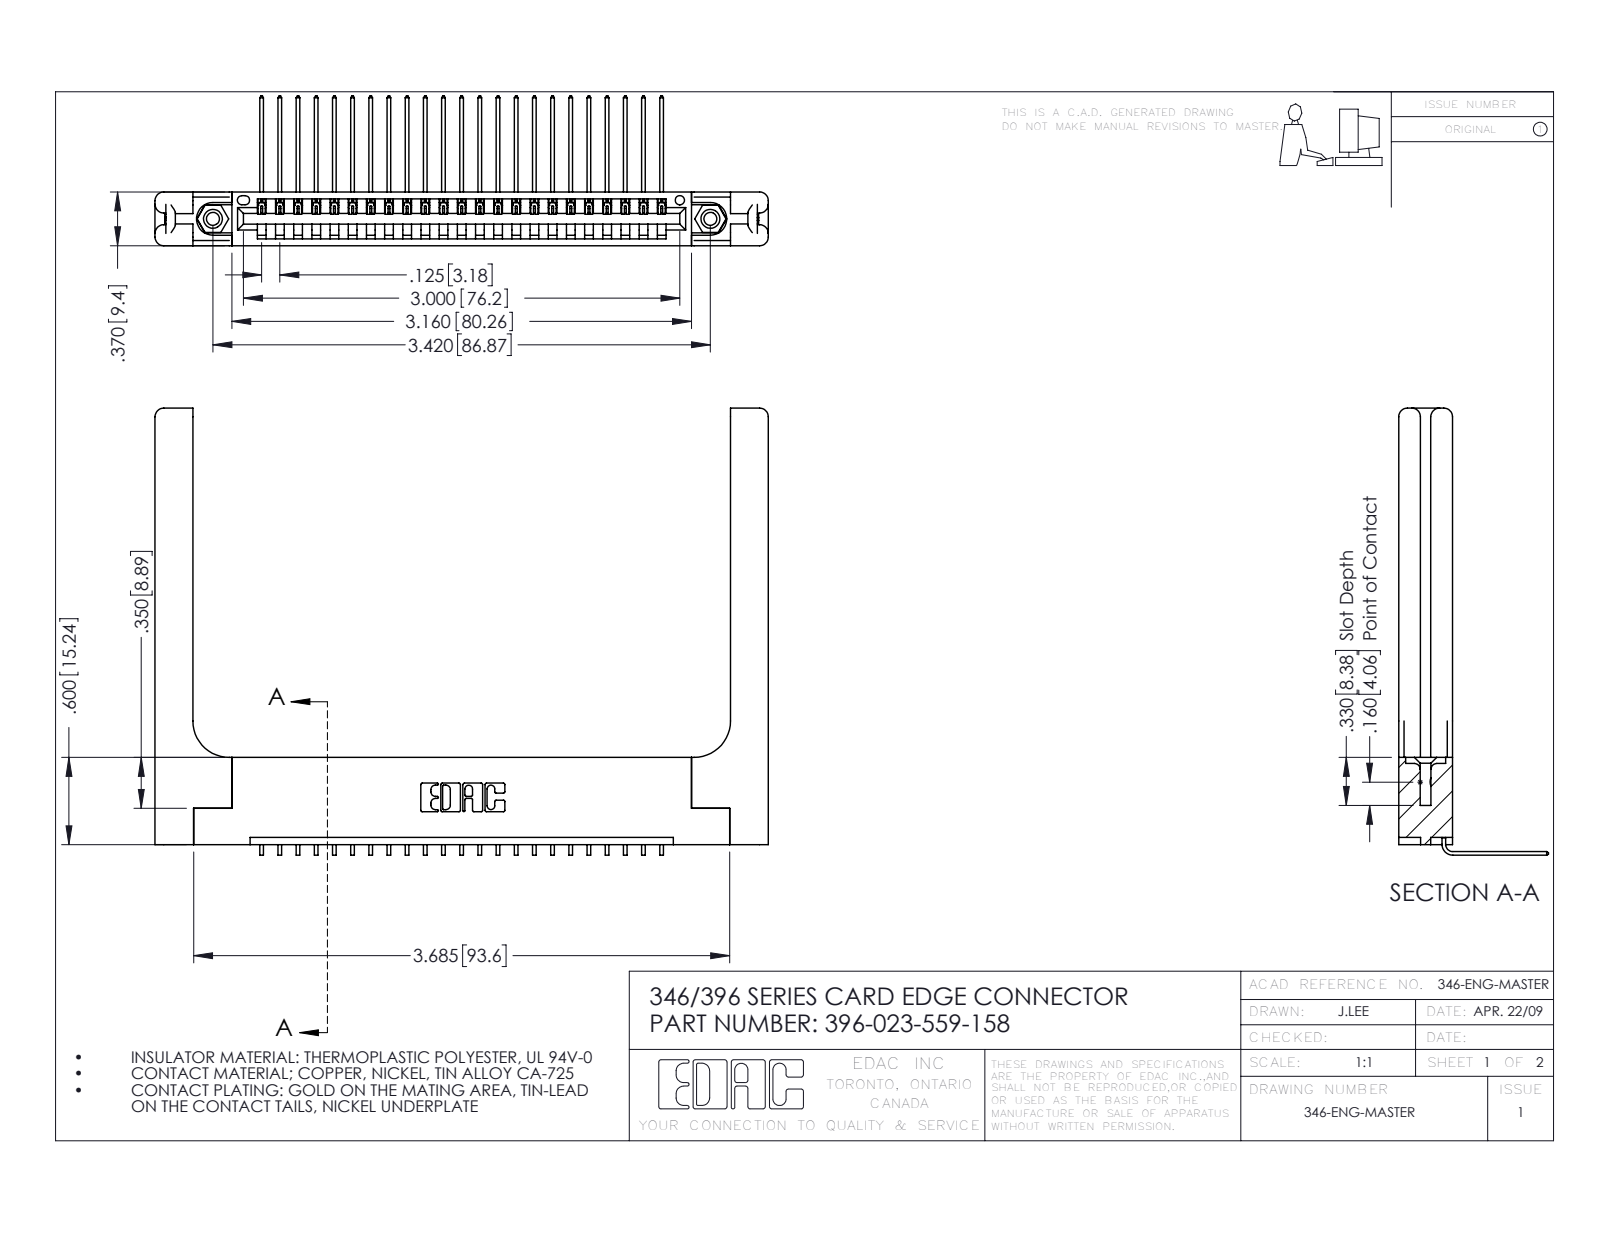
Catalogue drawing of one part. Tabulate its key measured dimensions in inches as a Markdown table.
| quantity | value |
| --- | --- |
| part name | 346-220-058_345-220-058; 346 Part_Flush Mounting Lugs - 0.156 Dia-TH; 396-023-559-158; 345-292-001_558 559 Tail - 1 (+1 more) |
| STEP written by | SolidWorks 2016 (CONFIG_CONTROL_DESIGN) |
| units | inches |
| bodies | 28 solids, 1758 faces (1190 planar, 508 cylindrical, 60 other) |
| overall size | 4.216 × 3.073 × 1.03 |
| volume | 1.081 in³ |
| surface area | 28.16 in² |
| round holes (diameter × count) | 0.089 × 2, 0.125 × 2, 0.156 × 2, 0.064 × 1 |
| round bosses / shafts (diameter × count) | 0.155 × 2 |
| partial cylindrical surfaces (radius × count) | 0.006 × 46, 0.01 × 22, 0.06 × 16, 0.007 × 6, 0.031 × 6, 0.026 × 3, 0.03 × 2, 0.031 × 2 |
| main face-to-face distances | 0.37, 0.072, 0.048, 0.322, 0.15, 0.148, 0.25, 0.025, 0.298, 0.102 |
| hole center spacings | 0.246, 3.212, 3.42 |
